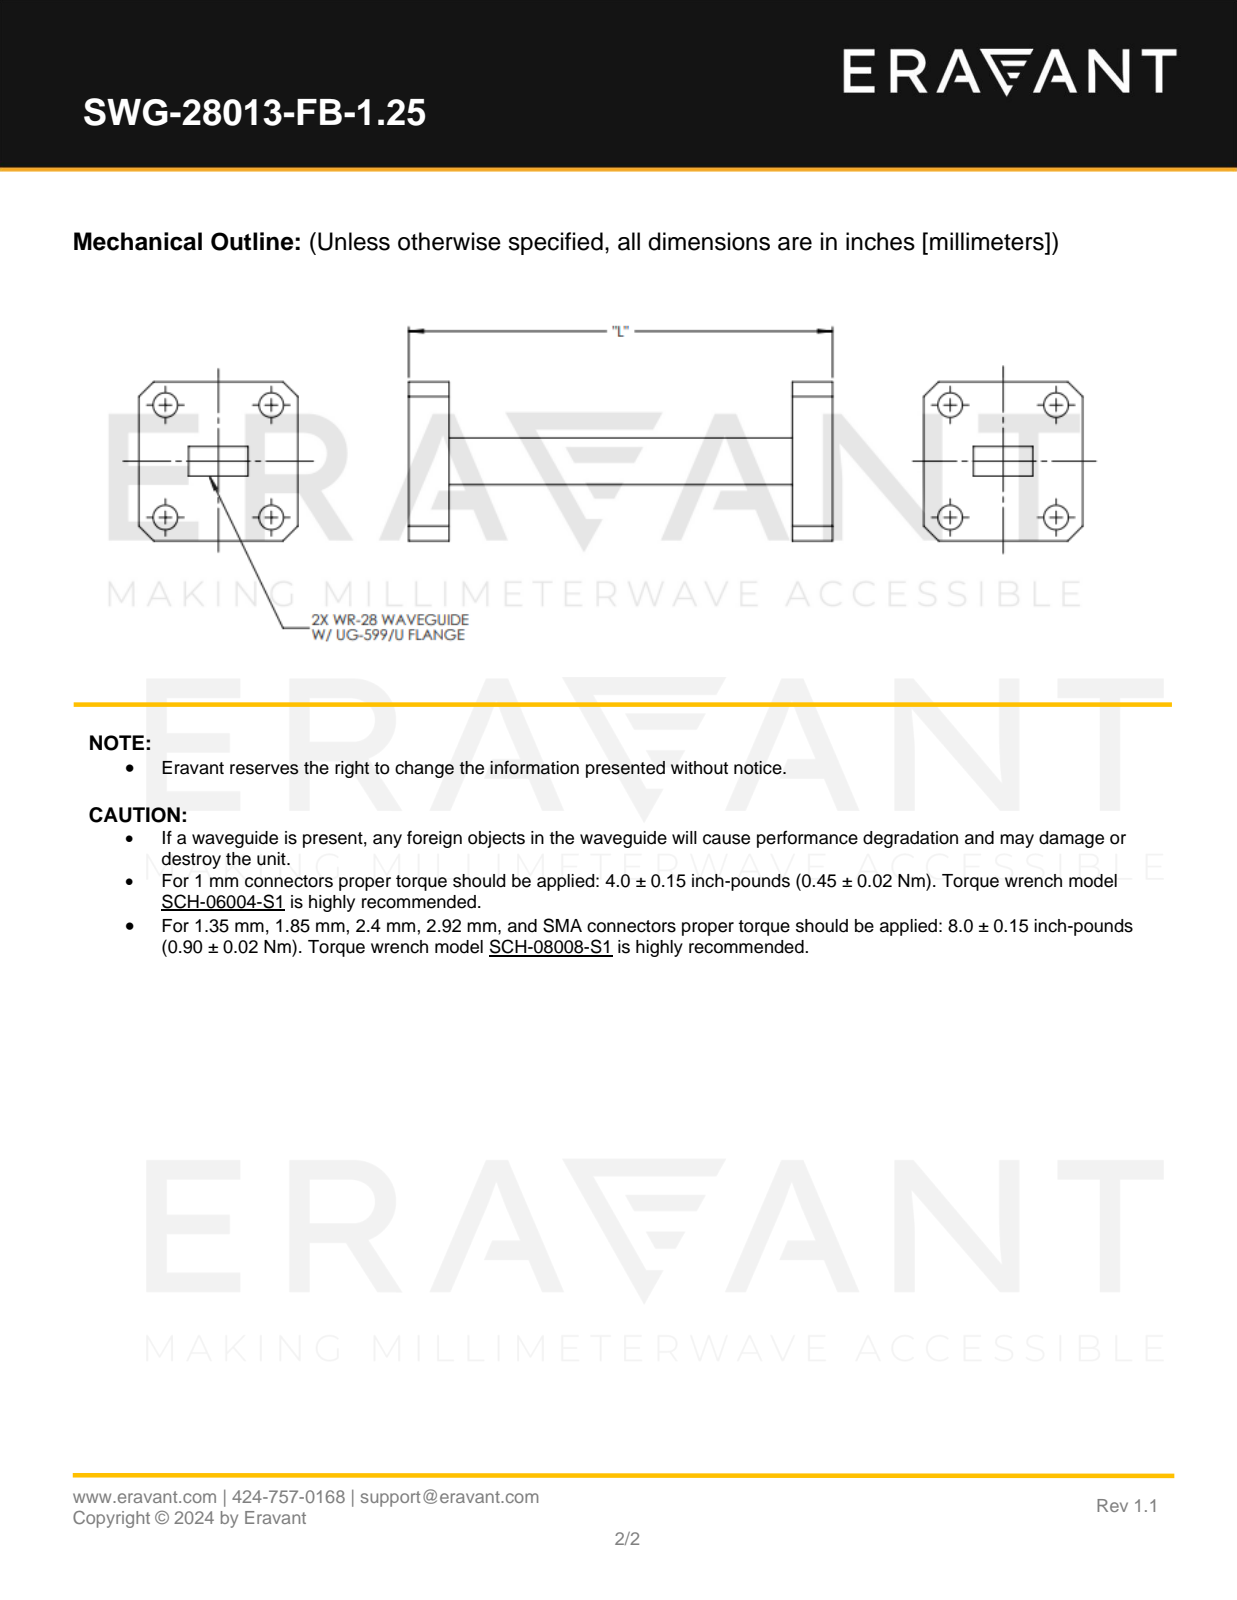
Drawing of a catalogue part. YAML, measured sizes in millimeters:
part_name: "SWG-28013-FB-1.25"
step_written_by: "SolidWorks 2021 (CONFIG_CONTROL_DESIGN)"
units: millimeters
bodies: {solids: 1, faces: 50, planar: 34, cylindrical: 16, other: 0}
overall_size: [31.8, 19.1, 19.1]
volume: 4290
surface_area: 2930
round_holes:
  - {diameter: 2.9, count: 4}
face_to_face_distances: [4.8, 26.9, 31.8, 22.1, 19.1, 5.6, 5, 14.1, 6.7, 12.3]
hole_center_spacings: [12.7, 13.5, 18.5]
